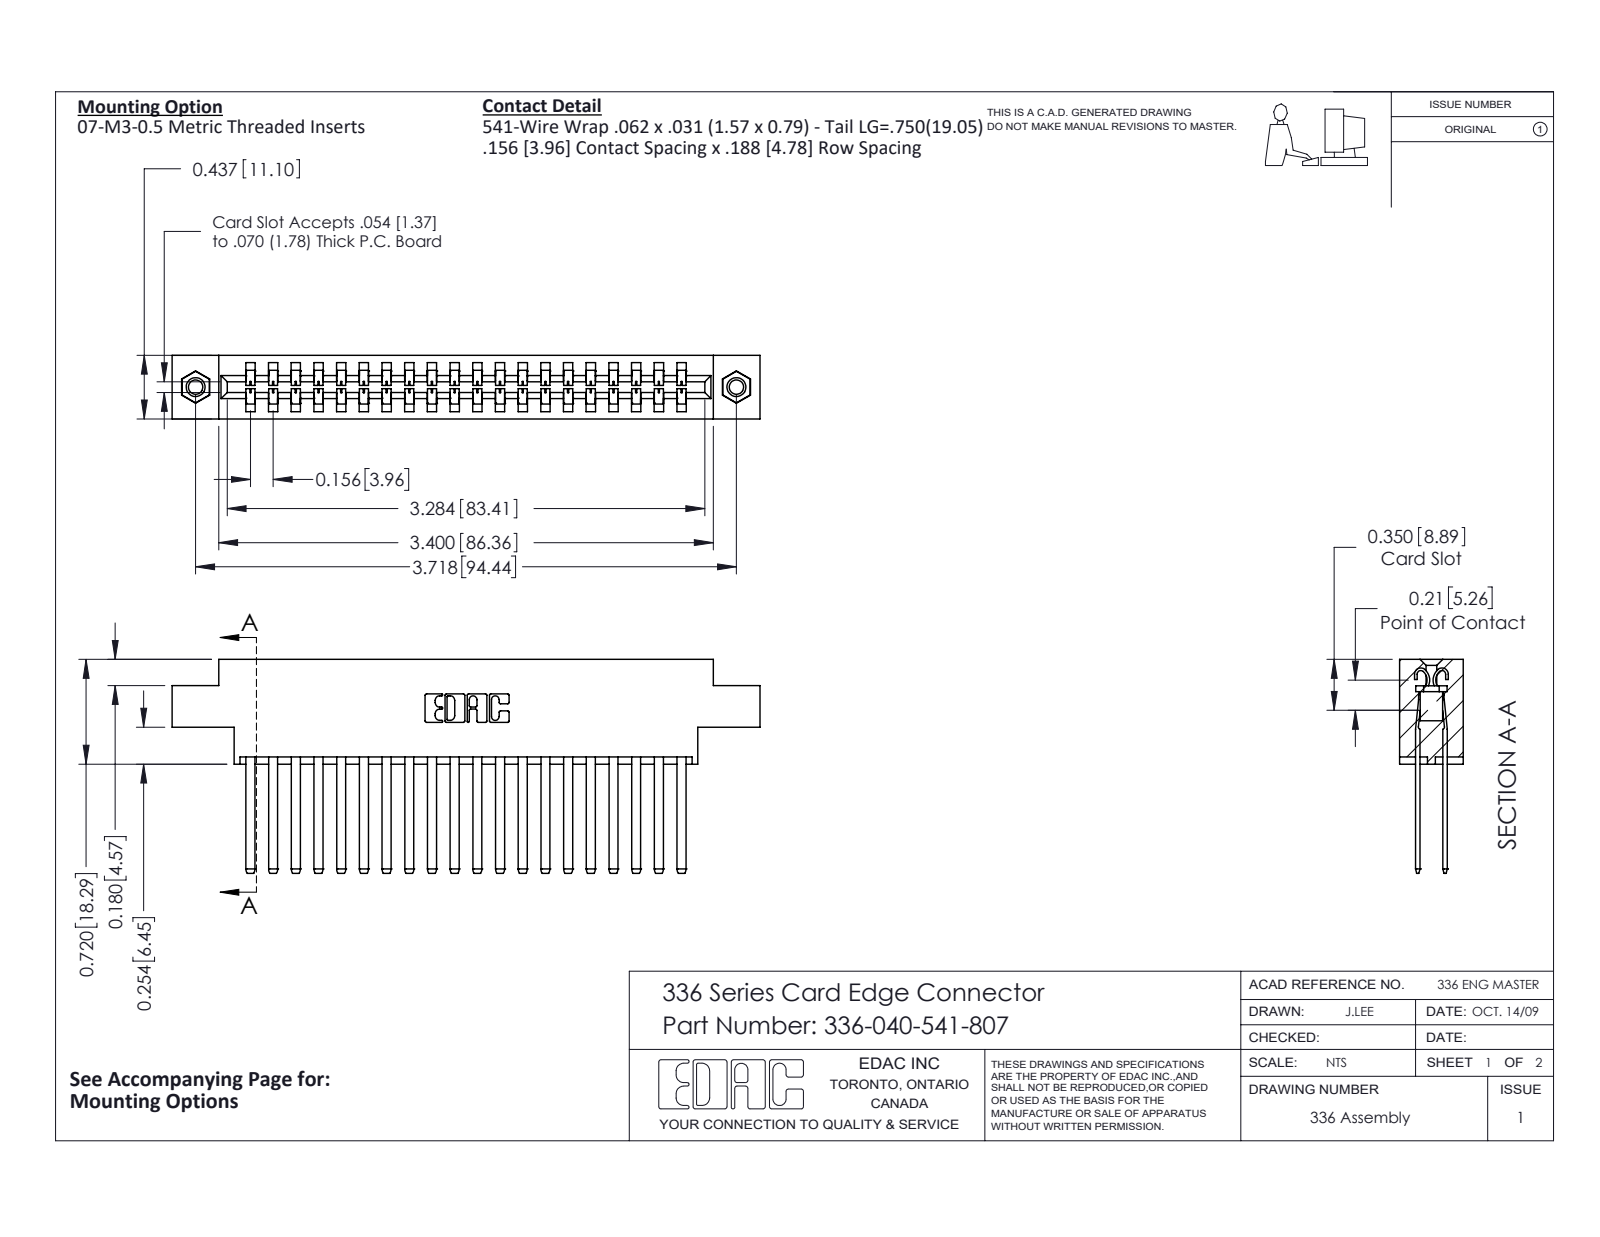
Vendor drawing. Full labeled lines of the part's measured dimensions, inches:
Part name (STEP PRODUCT): 336 Part_Offset - .156 Dia - TI; 345-250-001_345-250-005-103; 336-290-001_336-290-541; 336-040-541-807
STEP written by: SolidWorks 2020 (CONFIG_CONTROL_DESIGN)
Units: inches
Bodies: 43 solids, 1858 faces (1146 planar, 696 cylindrical, 16 other)
Overall size (bounding box): 4.041 × 1.47 × 0.437
Volume: 0.922 in³ · Surface area: 29.44 in²
Round holes (diameter × count): ⌀0.098 ×2, ⌀0.125 ×2, ⌀0.156 ×2
Round bosses / shafts (diameter × count): ⌀0.155 ×2
Partial cylindrical surfaces — rounded edges, fillets, slot ends (radius × count): R0.004 ×80, R0.056 ×40, R0.01 ×22, R0.007 ×6, R0.031 ×6, R0.022 ×4, R0.04 ×4, R0.026 ×3
Main face-to-face distances: 0.188, 0.328, 0.14, 0.297, 0.109, 0.031, 0.437, 0.033, 0.156, 0.181
Hole centre spacings: 3.718
